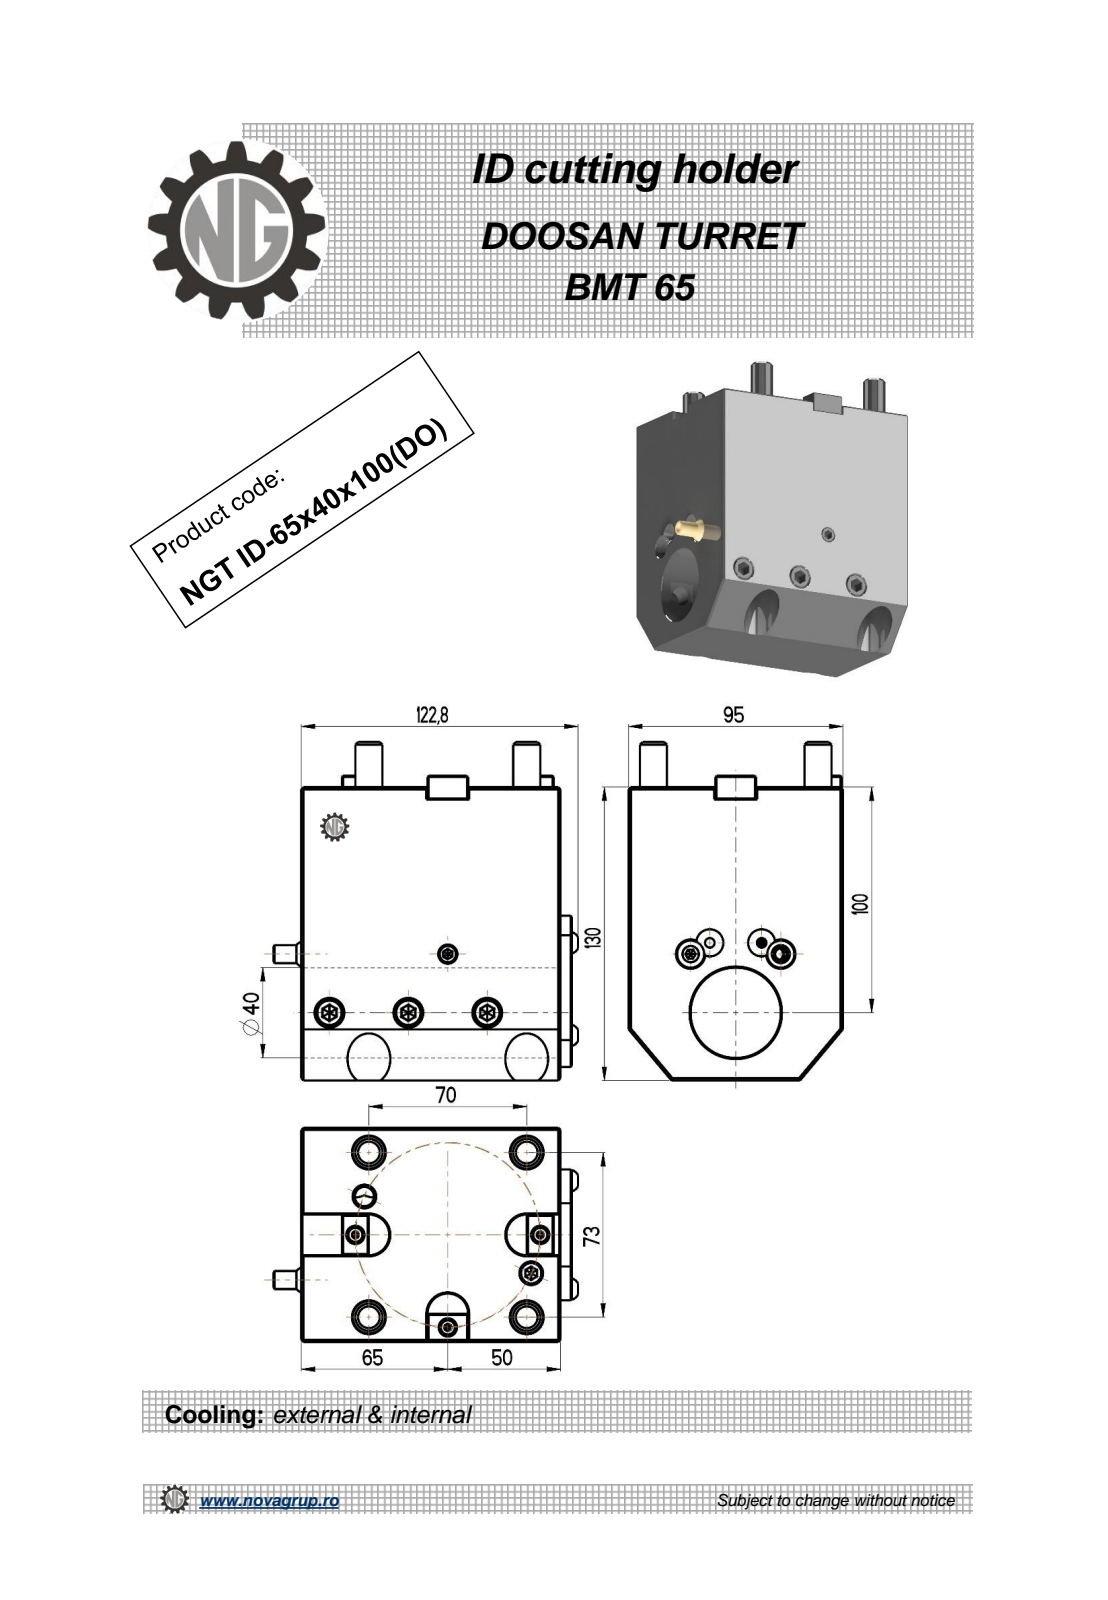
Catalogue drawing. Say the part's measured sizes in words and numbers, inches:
The part is named "NGT_ID_65_40_100_DO". Its 3-D file was written by "PRO/ENGINEER BY PARAMETRIC TECHNOLOGY CORPORATION, 2010280 (CONFIG_CONTROL_DESIGN)". It is 1 solid with 373 faces: 203 planar, 73 cylindrical and 97 other. Overall it measures 5.906 by 5.319 by 3.74 inches. Its volume is 75.79 cubic inches and its surface area 152.5 square inches. Round holes: 3 of diameter 0.402, 1 of diameter 0.197, 1 of diameter 0.335, 1 of diameter 1.575. Round bosses or shafts: 4 of diameter 0.472, 1 of diameter 0.315. Partial cylindrical surfaces (rounded edges, fillets, slot ends): 36 of radius 0.024, 6 of radius 0.02, 3 of radius 0.354. The main face-to-face distances are 3.74, 4.528, 5.118, 0.197, 4.724, 0.787, 4.921, 1.496, 0.709, 5.315. The hole center spacings are 1.378, 1.291, 2.756.
